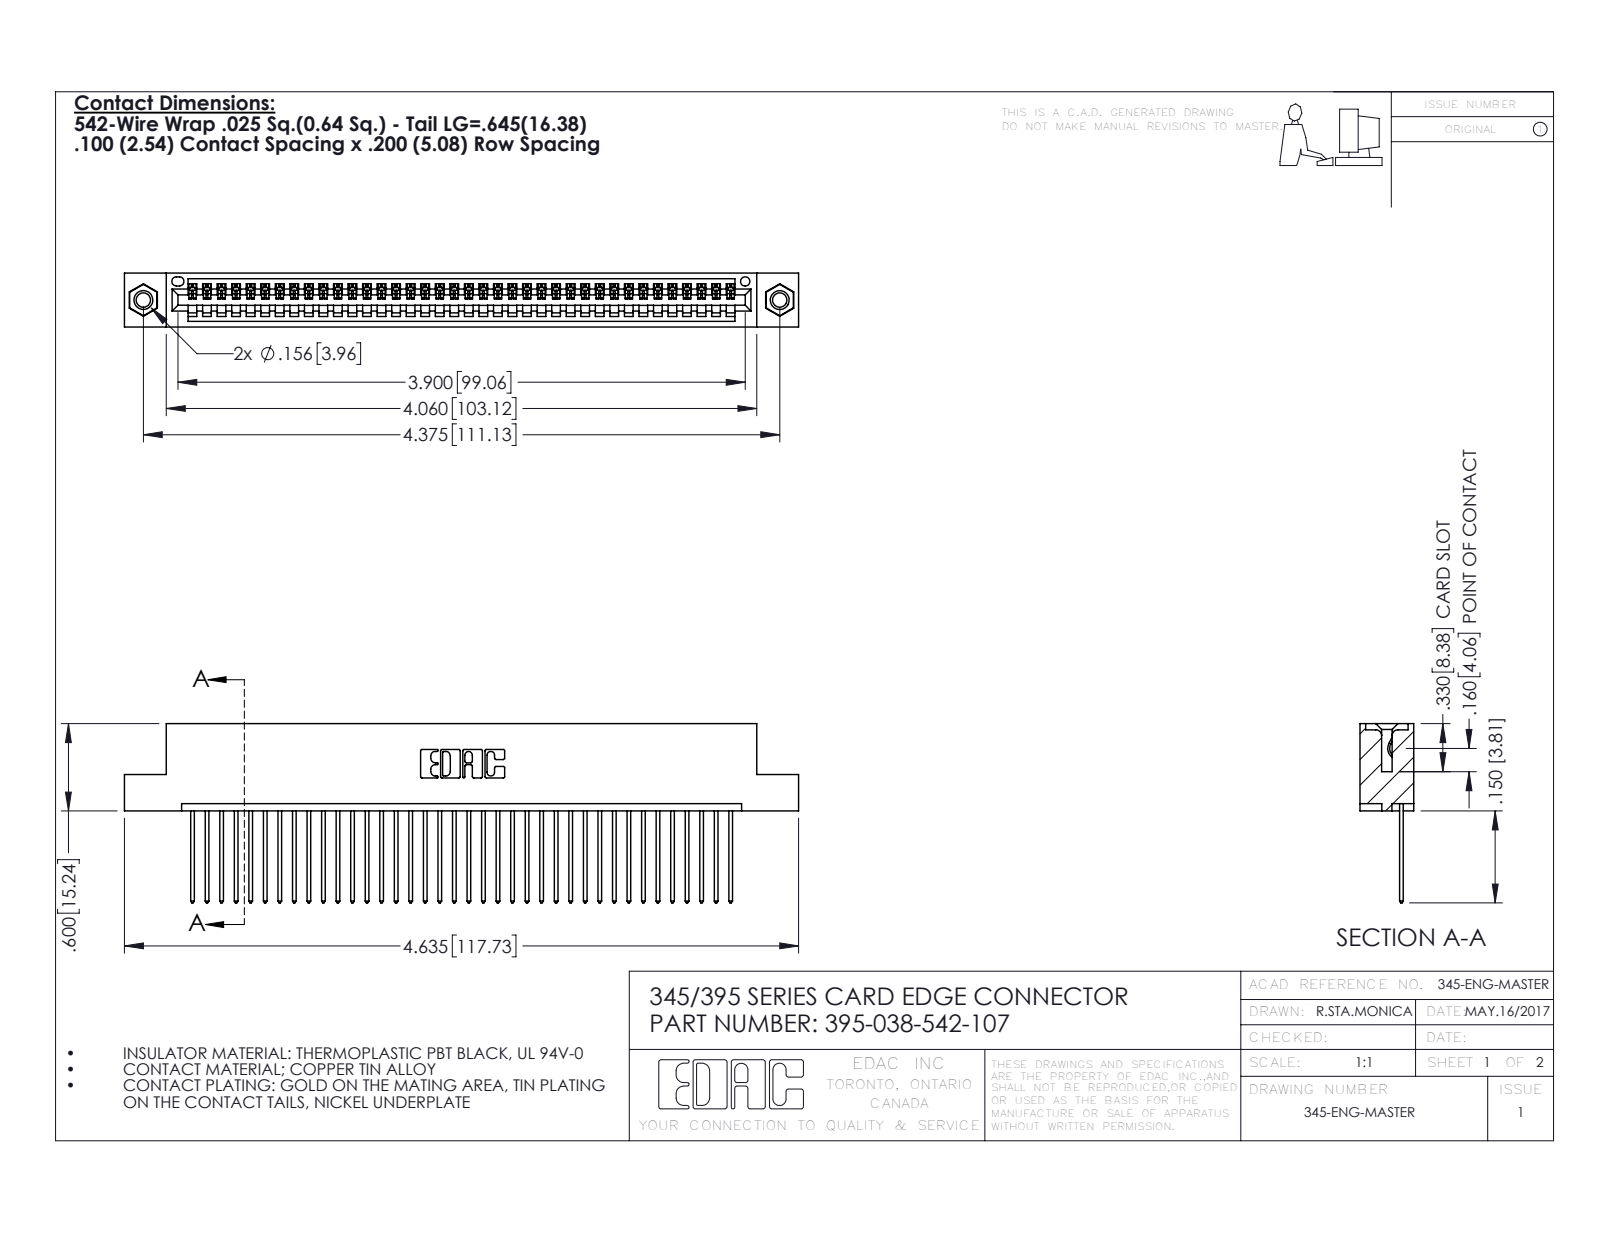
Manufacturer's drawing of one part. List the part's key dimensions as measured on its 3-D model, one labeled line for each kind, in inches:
Part name (STEP PRODUCT): 345-250-001_345-250-005-103; 345-292-001_345-293-142; 395-038-542-107; 345 Part_Flush Mounting Lugs - 0.156 Dia-TI
STEP written by: SolidWorks 2016 (CONFIG_CONTROL_DESIGN)
Units: inches
Bodies: 41 solids, 2390 faces (1632 planar, 742 cylindrical, 16 other)
Overall size (bounding box): 4.635 × 1.232 × 0.37
Volume: 0.685 in³ · Surface area: 23.91 in²
Round holes (diameter × count): ⌀0.098 ×2, ⌀0.125 ×2, ⌀0.156 ×2, ⌀0.064 ×1
Round bosses / shafts (diameter × count): ⌀0.155 ×2
Partial cylindrical surfaces — rounded edges, fillets, slot ends (radius × count): R0.006 ×76, R0.01 ×76, R0.01 ×22, R0.007 ×6, R0.031 ×6, R0.026 ×3, R0.031 ×2, R0.04 ×2
Main face-to-face distances: 0.072, 0.298, 0.37, 0.2, 0.098, 0.272, 0.025, 0.225, 0.149, 0.072
Hole centre spacings: 0.27, 4.139, 4.375
